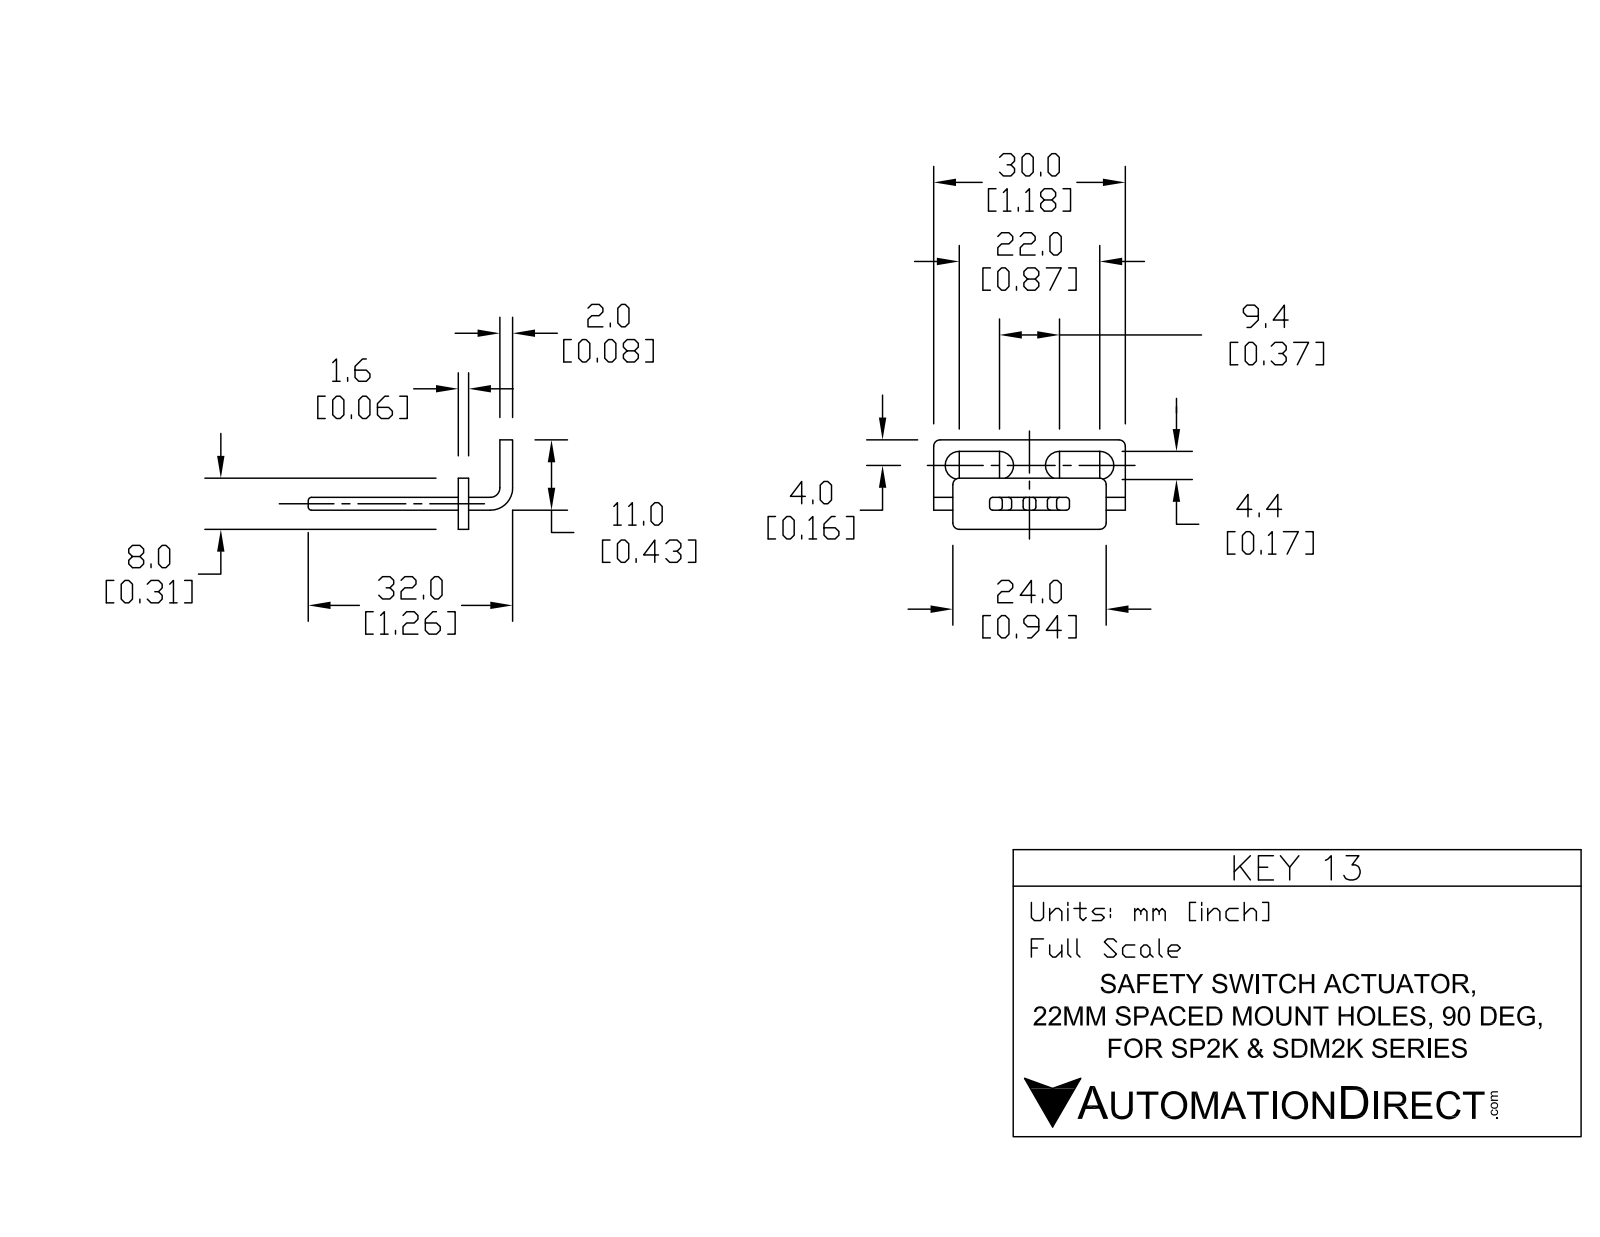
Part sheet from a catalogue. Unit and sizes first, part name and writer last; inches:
Units: inches
Overall size (bounding box): 1.26 × 1.181 × 0.551
Partial cylindrical surfaces — rounded edges, fillets, slot ends (radius × count): R0.02 ×42, R0.039 ×8, R0.008 ×4, R0.059 ×4, R0.087 ×4, R0.031 ×1, R0.11 ×1
Main face-to-face distances: 0.079, 0.335, 0.063, 0.256, 0.319, 0.398, 0.118, 0.433, 0.197, 0.551
Volume: 0.087 in³ · Surface area: 3.311 in²
Bodies: 2 solids, 164 faces (58 planar, 78 cylindrical, 28 other)
Part name (STEP PRODUCT): KEY13
STEP written by: SolidWorks 2019 (CONFIG_CONTROL_DESIGN)
